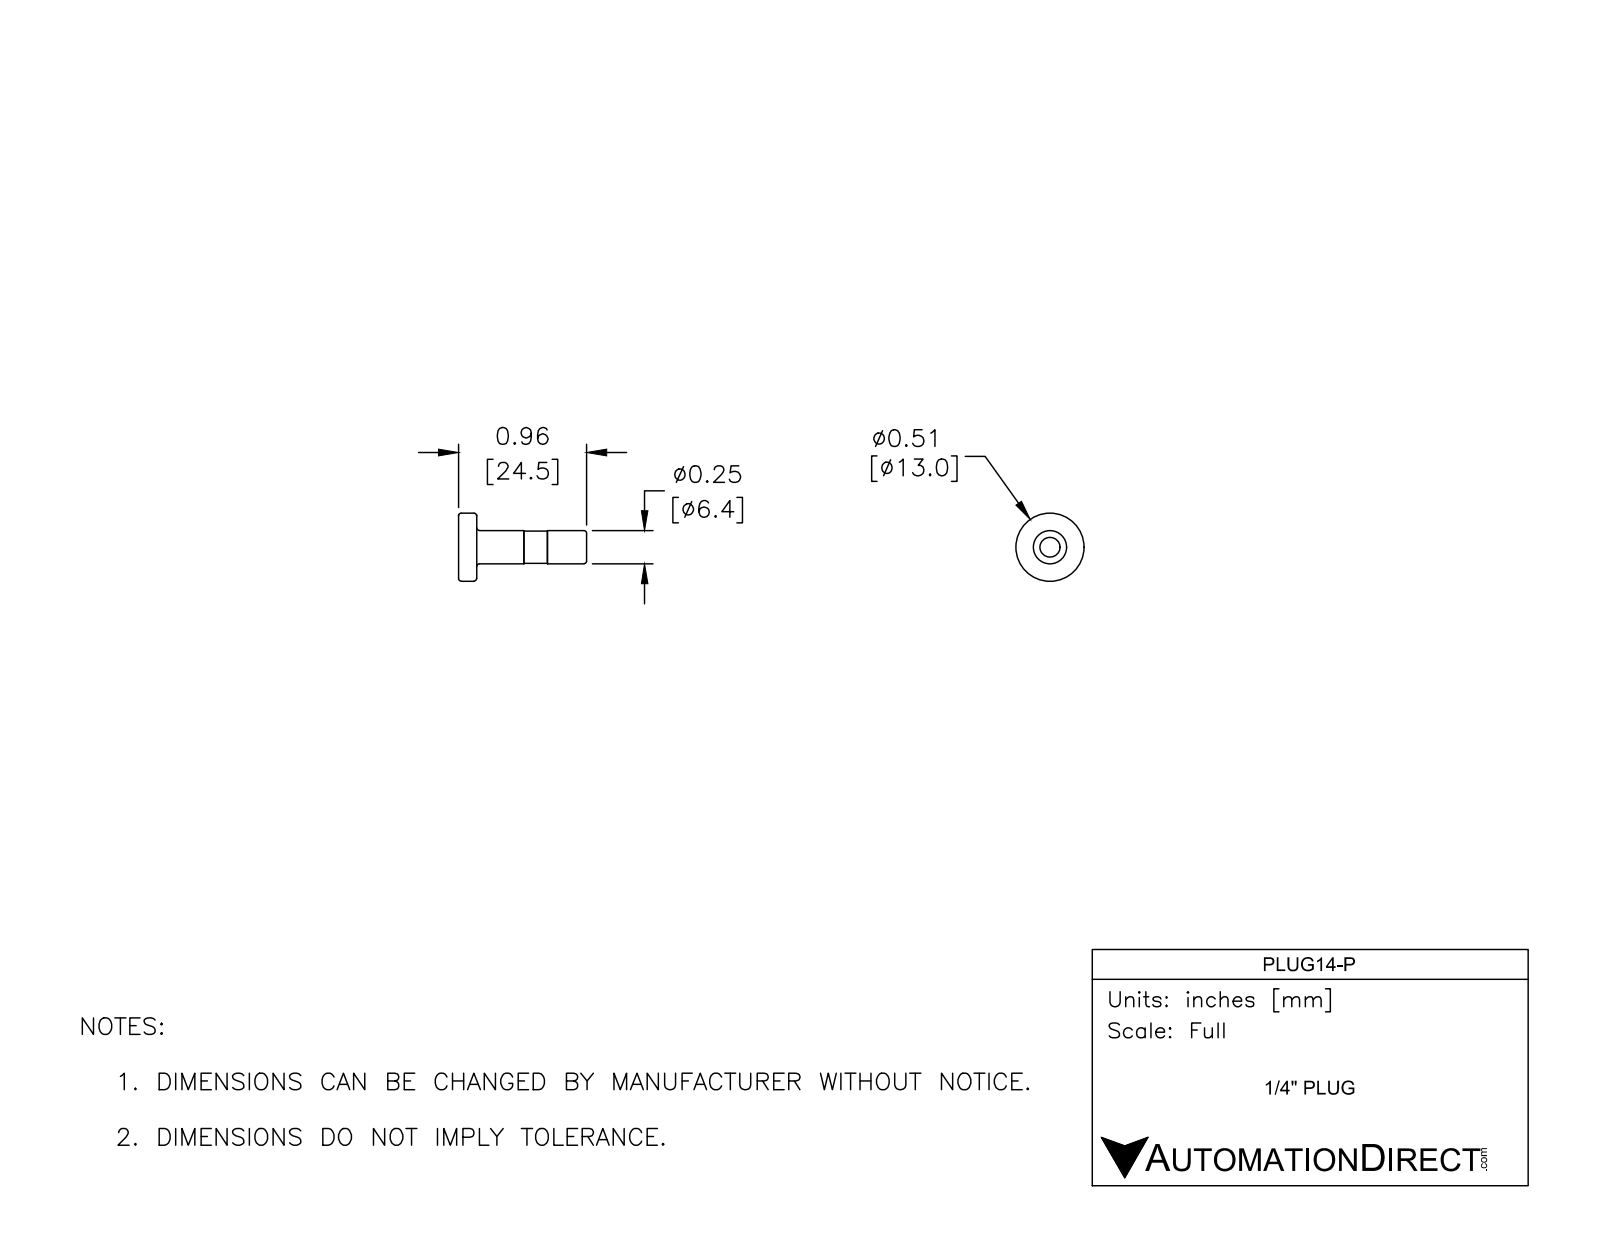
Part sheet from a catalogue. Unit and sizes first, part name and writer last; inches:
Units: inches
Overall size (bounding box): 0.965 × 0.512 × 0.512
Round holes (diameter × count): ⌀0.15 ×1
Round bosses / shafts (diameter × count): ⌀0.512 ×1, ⌀0.25 ×1, ⌀0.244 ×1
Main face-to-face distances: 0.118, 0.02, 0.138, 0.965, 0.945, 0.827, 0.512, 0.492, 0.374, 0.453
Volume: 0.05 in³ · Surface area: 1.65 in²
Bodies: 1 solid, 38 faces (6 planar, 12 cylindrical, 20 other)
Part name (STEP PRODUCT): PLUG14-P
STEP written by: SolidWorks 2017 (AUTOMOTIVE_DESIGN)
